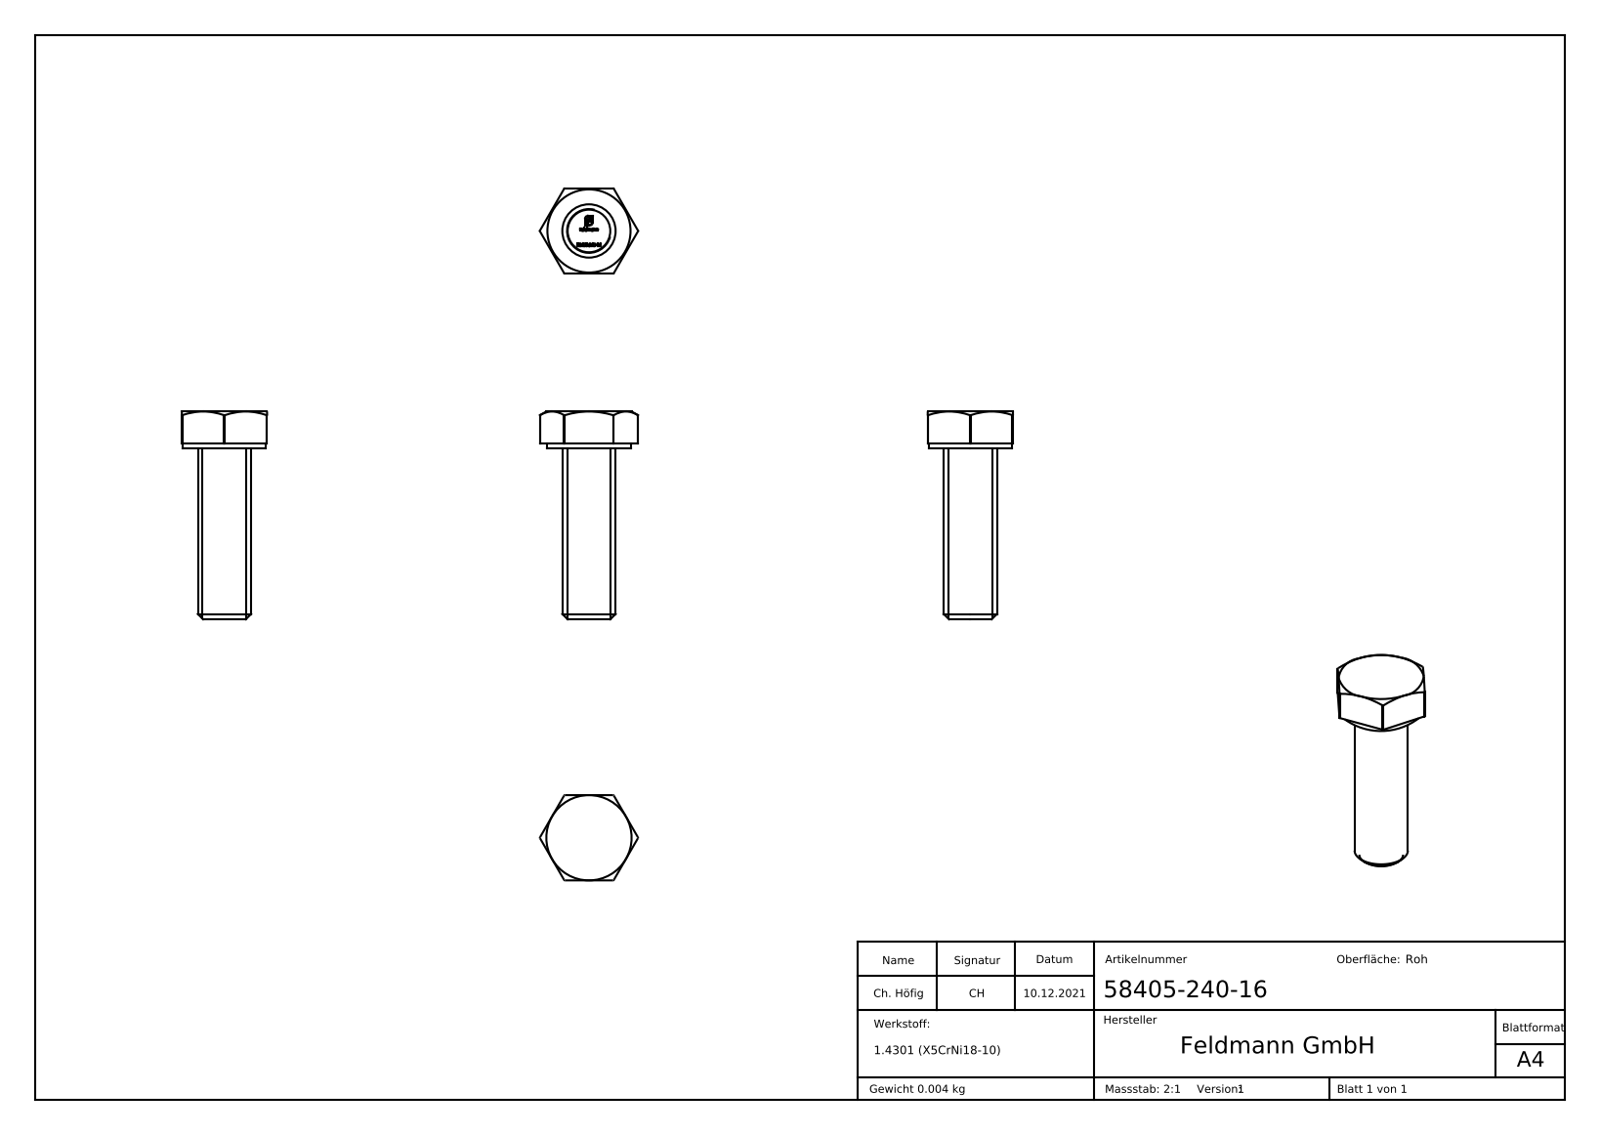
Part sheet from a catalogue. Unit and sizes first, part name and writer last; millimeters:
Units: millimetres
Overall size (bounding box): 19.5 × 9.21 × 8
Round bosses / shafts (diameter × count): ⌀7.8 ×1, ⌀5 ×1
Partial cylindrical surfaces — rounded edges, fillets, slot ends (radius × count): R0.1 ×6
Main face-to-face distances: 8, 3.5, 16, 19.5, 0.5, 16.5, 3, 15.9, 16.4, 19.4
Volume: 502 mm³ · Surface area: 453 mm²
Bodies: 1 solid, 327 faces (178 planar, 8 cylindrical, 141 other)
Part name (STEP PRODUCT): DIN 933 M2-M36
STEP written by: SolidWorks 2018 (CONFIG_CONTROL_DESIGN)
